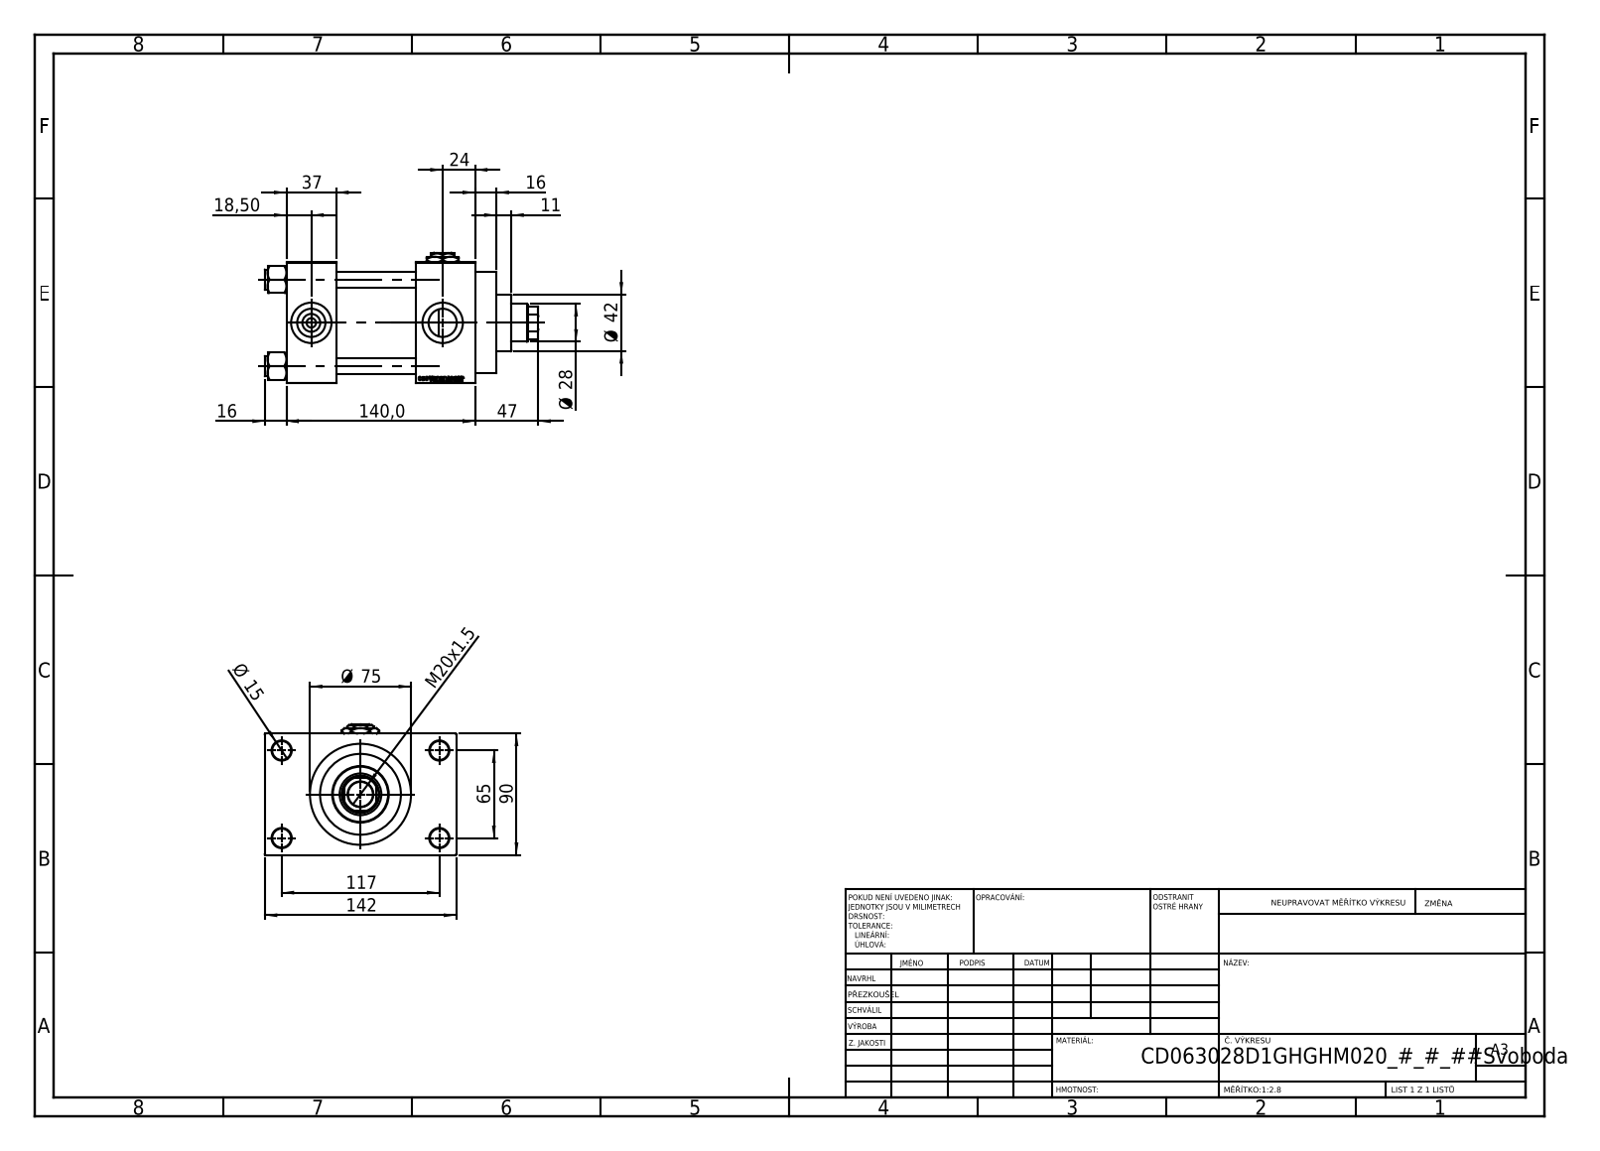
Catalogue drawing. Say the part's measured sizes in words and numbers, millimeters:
The part is named "Zatka_pro_OIL_PORT; V215CD_VCP_D; V215CD_D_TYCINKA; V215CD_VC_A (+2 more)". Its 3-D file was written by "SolidWorks 2019 (CONFIG_CONTROL_DESIGN)". It is 12 solids with 1151 faces: 521 planar, 92 cylindrical and 538 other. Overall it measures 203 by 142 by 97 millimeters. Its volume is 1 093 000 cubic millimeters and its surface area 202 170 square millimeters. Round holes: 4 of diameter 12, 4 of diameter 14, 3 of diameter 20.96, 3 of diameter 30, 2 of diameter 7, 1 of diameter 18.5, 1 of diameter 28, 1 of diameter 31, 1 of diameter 50, 1 of diameter 60, 1 of diameter 63. Round bosses or shafts: 4 of diameter 15, 1 of diameter 75, 1 of diameter 69, 1 of diameter 42. Partial cylindrical surfaces (rounded edges, fillets, slot ends): 1 of radius 13.5. The main face-to-face distances are 90, 59, 37, 96, 140, 103, 44, 26, 116, 16. The hole center spacings are 26.35, 45.47, 64.3, 66.92, 69.81, 90.65, 111.34, 65.
